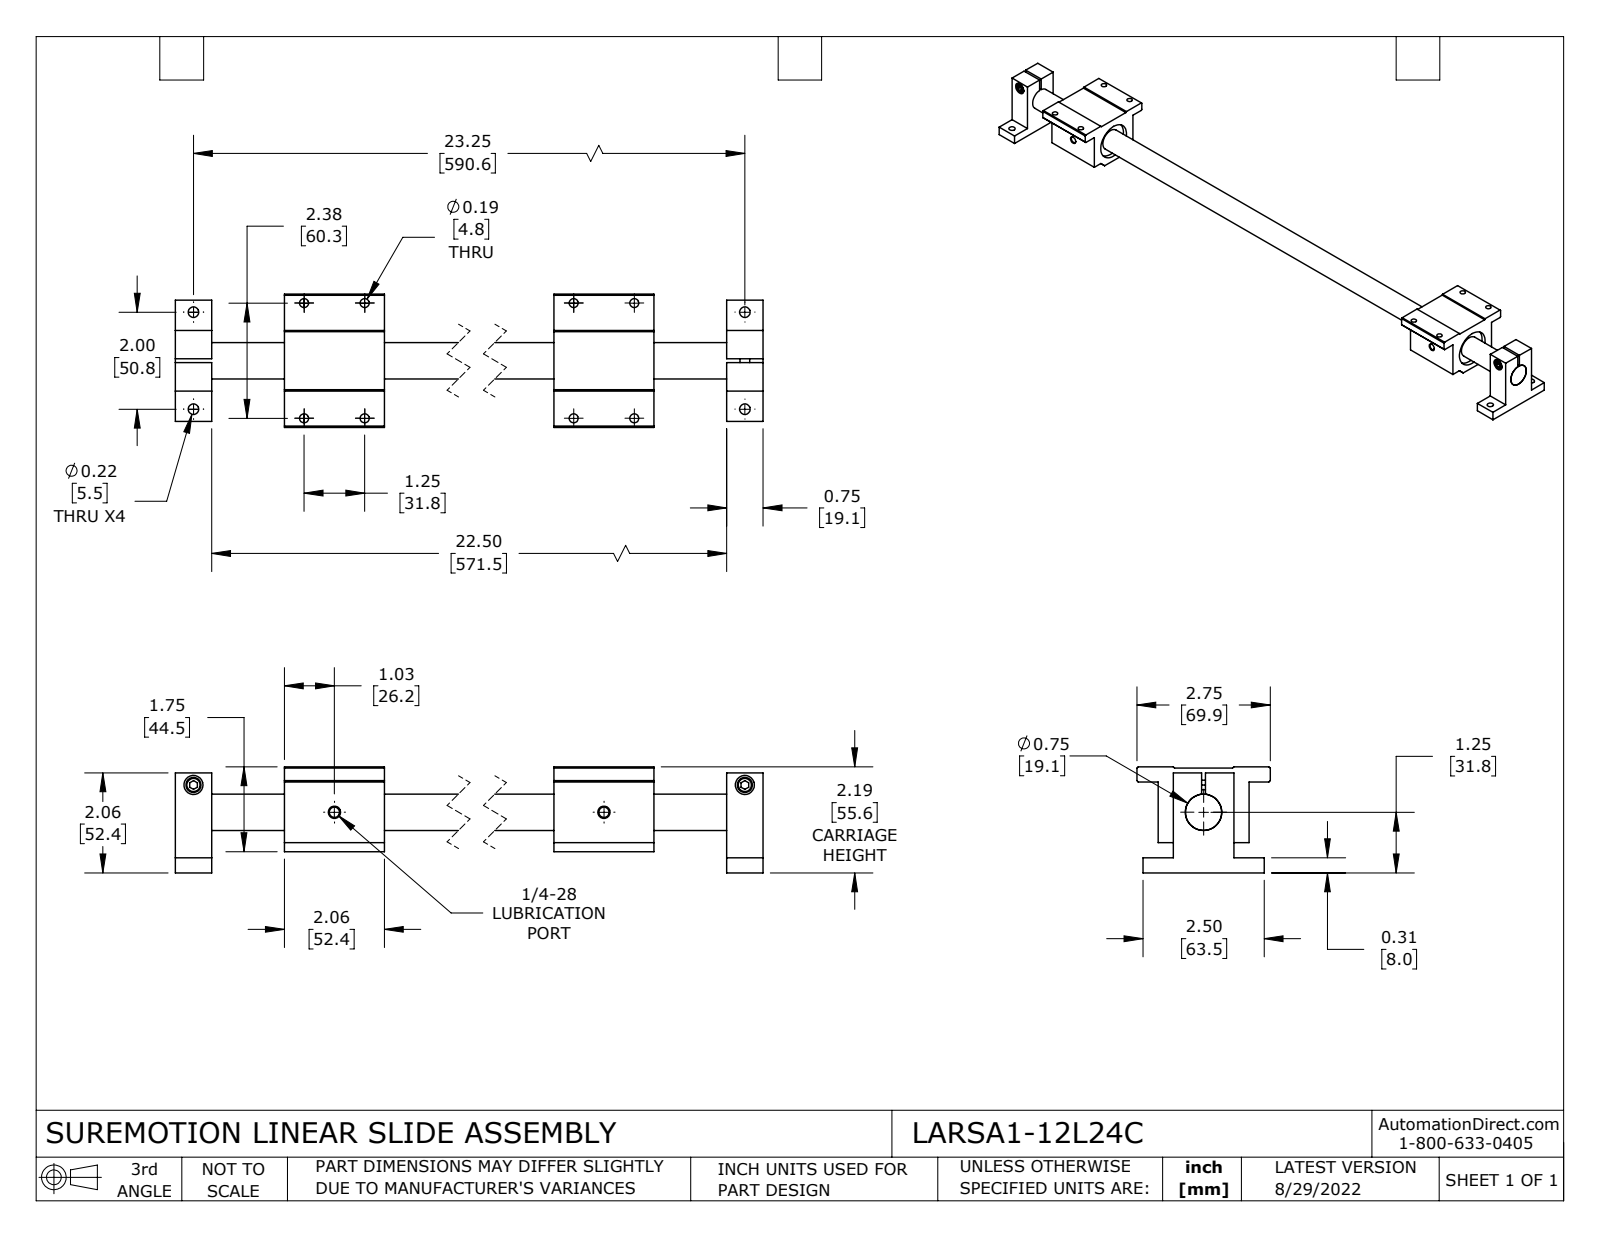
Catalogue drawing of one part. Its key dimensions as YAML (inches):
part_name: "LARSA1-12L24C-RAIL; LARSACC-002; LARSA1-12L24C"
step_written_by: "SolidWorks 2021 (CONFIG_CONTROL_DESIGN)"
units: inches
bodies: {solids: 7, faces: 166, planar: 98, cylindrical: 58, other: 10}
overall_size: [24, 2.75, 2.187]
volume: 25.79
surface_area: 147.4
round_holes:
  - {diameter: 0.188, count: 8}
  - {diameter: 0.218, count: 4}
  - {diameter: 0.213, count: 2}
  - {diameter: 0.394, count: 2}
  - {diameter: 0.75, count: 1}
  - {diameter: 1.25, count: 1}
round_bosses_or_shafts:
  - {diameter: 0.312, count: 2}
face_to_face_distances: [1.563, 0.75, 2.063, 17.437, 1.75, 0.313, 1.876, 23.25, 0.028, 0.313]
hole_center_spacings: [1.25, 2.376, 2.684, 17.437, 17.598, 23.25, 2, 2.289]
